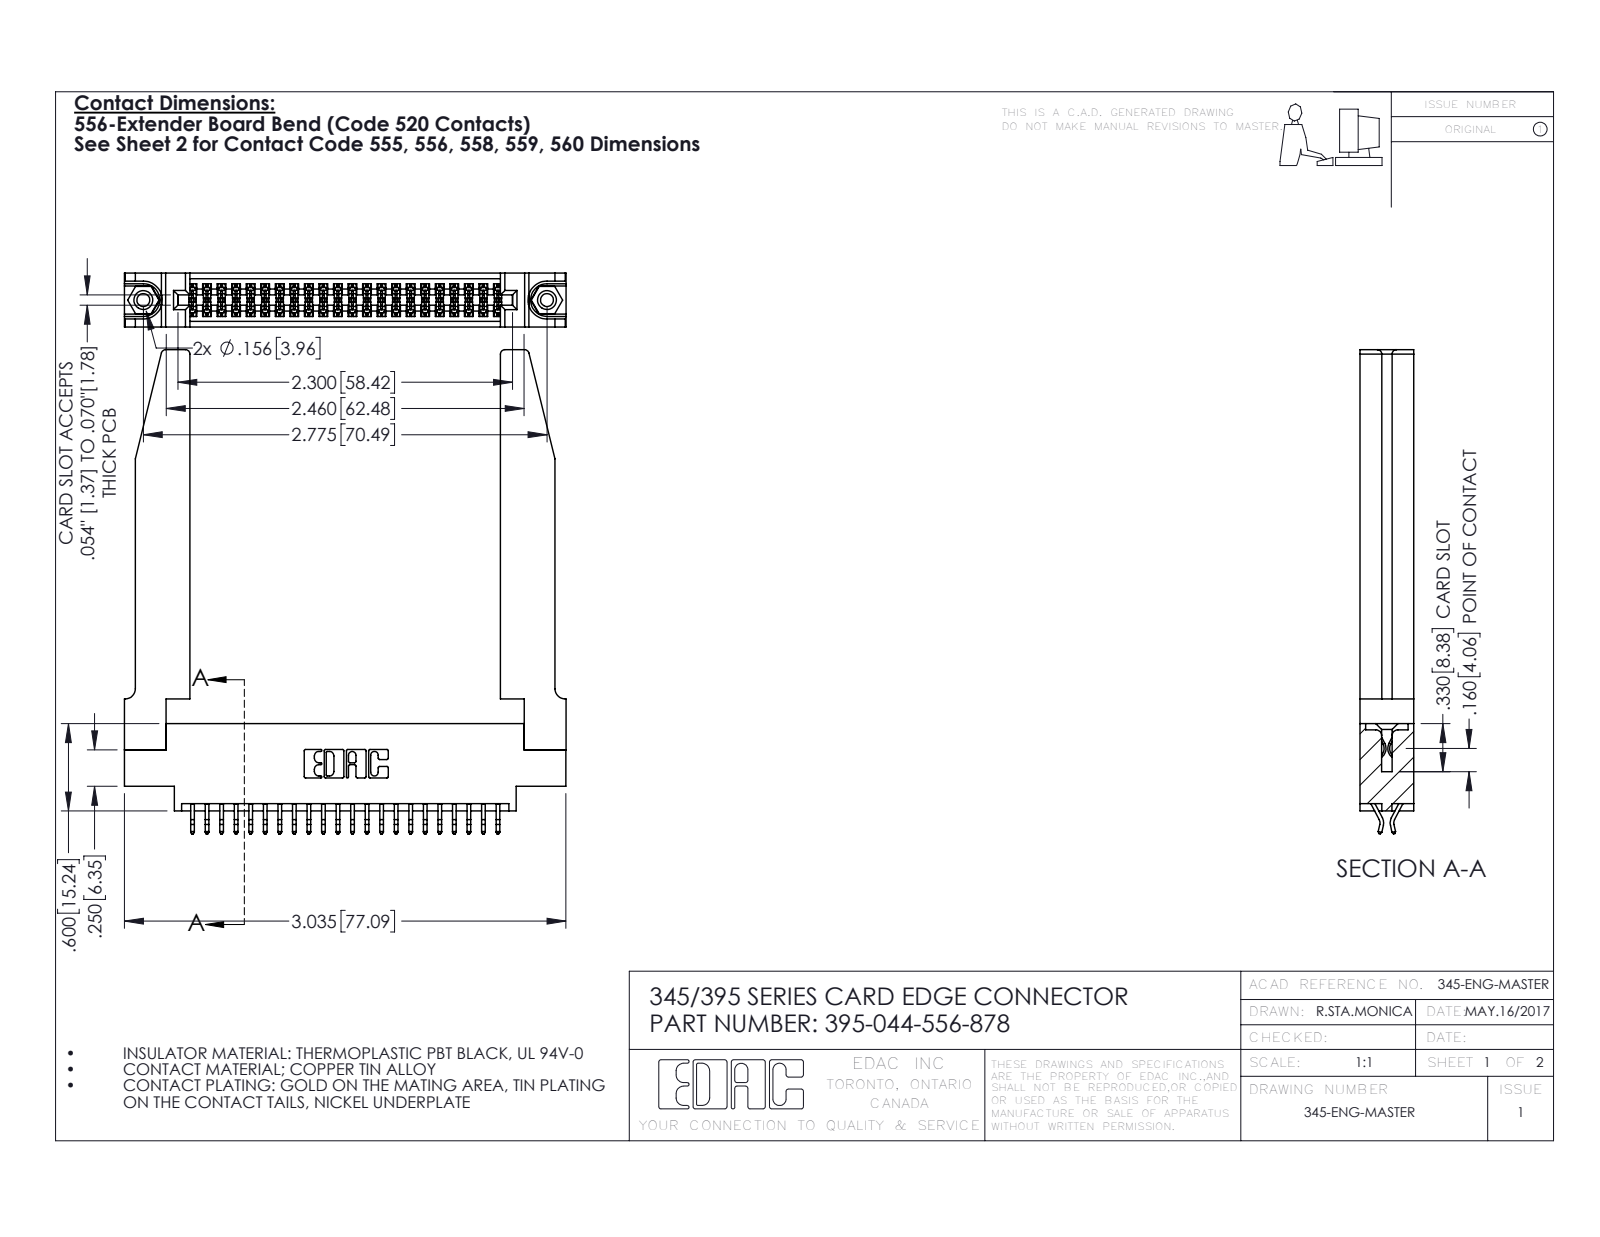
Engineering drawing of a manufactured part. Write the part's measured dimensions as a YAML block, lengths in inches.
part_name: "345-220-078_345-220-078; 345-292-001_556 Tail; 395-044-556-878; 345 Part_0.170 Offset - 0.156 Dia-TH (+1 more)"
step_written_by: "SolidWorks 2016 (CONFIG_CONTROL_DESIGN)"
units: inches
bodies: {solids: 49, faces: 2828, planar: 1854, cylindrical: 922, other: 52}
overall_size: [3.327, 3.036, 0.37]
volume: 0.913
surface_area: 26.64
round_holes:
  - {diameter: 0.089, count: 2}
  - {diameter: 0.125, count: 2}
  - {diameter: 0.156, count: 2}
  - {diameter: 0.064, count: 1}
round_bosses_or_shafts:
  - {diameter: 0.155, count: 2}
partial_cylinders:
  - {radius: 0.006, count: 66}
  - {radius: 0.01, count: 22}
  - {radius: 0.03, count: 8}
  - {radius: 0.007, count: 6}
  - {radius: 0.031, count: 6}
  - {radius: 0.026, count: 3}
  - {radius: 0.01, count: 2}
  - {radius: 0.014, count: 2}
face_to_face_distances: [0.37, 0.072, 0.298, 0.025, 0.098, 0.272, 0.2, 0.225, 0.148, 0.15]
hole_center_spacings: [0.27, 2.541, 2.775]
